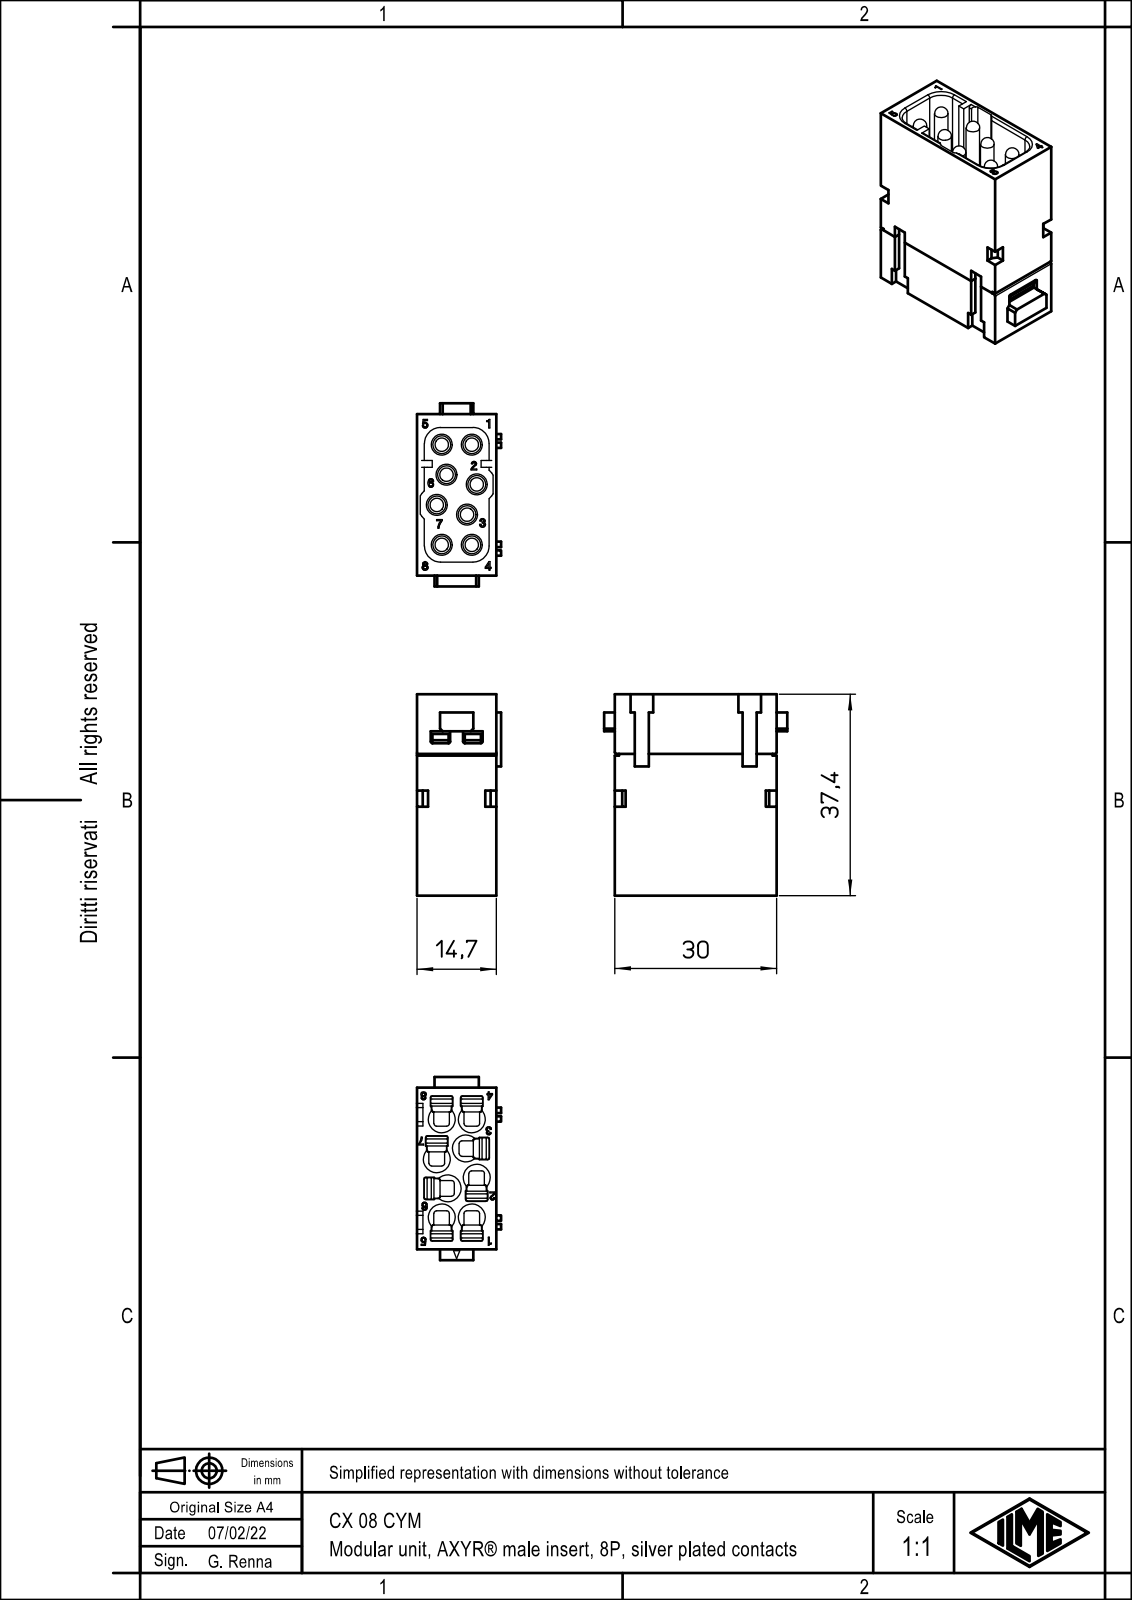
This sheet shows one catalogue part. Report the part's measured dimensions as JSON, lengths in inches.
{"part_name": "CX_08_CYM", "step_written_by": "Creo Elements/Direct Modeling 20.1B 02-Apr-2019 (C) Parametric Technology GmbH (AUTOMOTIVE_DESIGN)", "units": "inches", "bodies": {"solids": 1, "faces": 1222, "planar": 800, "cylindrical": 298, "other": 124}, "overall_size": [1.472, 1.339, 0.614], "volume_in3": 0.707, "surface_area_in2": 13.34, "round_bosses_or_shafts": [[0.154, 8], [0.098, 8]], "partial_cylinders_radius": [[0.008, 76], [0.016, 48], [0.02, 26], [0.012, 24], [0.004, 16], [0.098, 8], [0.079, 6], [0.118, 4]], "face_to_face_distances": [0.579, 1.181, 0.053, 0.526, 0.472, 0.035, 0.098, 1.122, 0.059, 1.083]}
